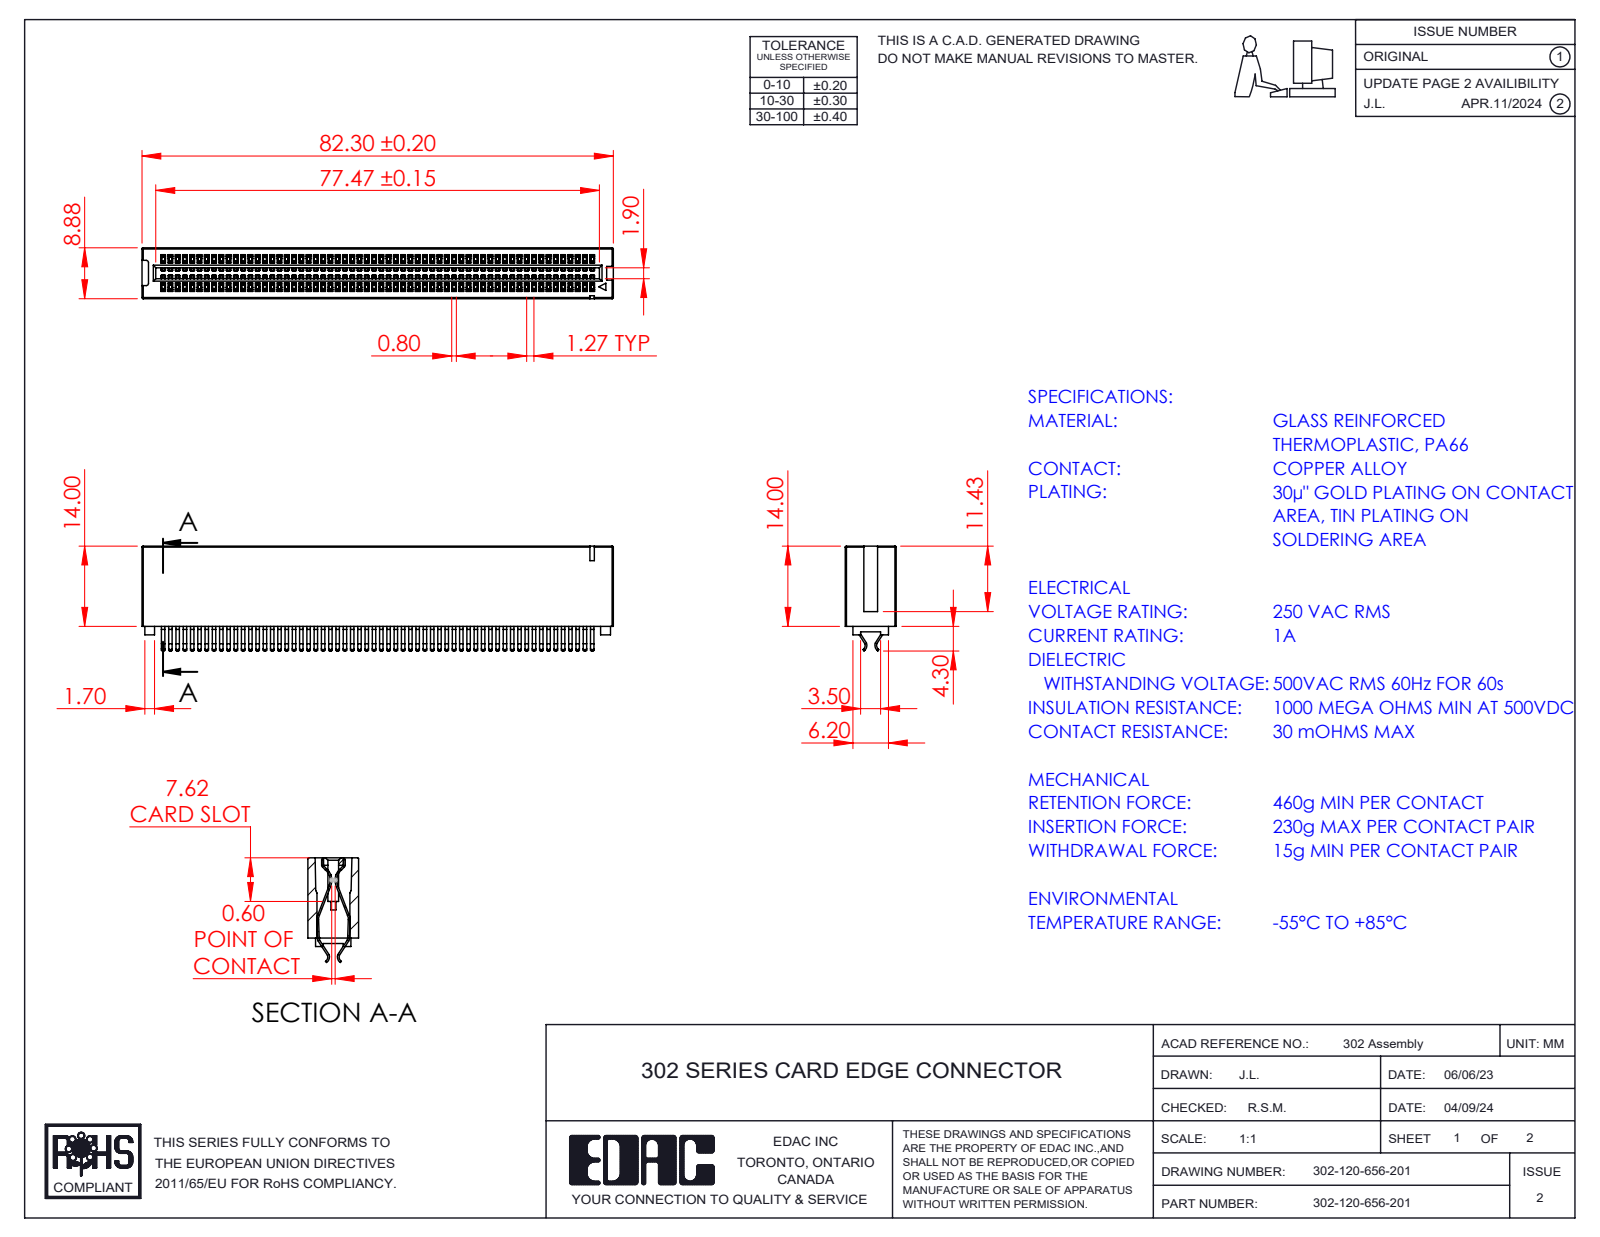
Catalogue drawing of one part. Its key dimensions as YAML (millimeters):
part_name: "302-120-656-201; Contact_302-290-X56; HSG_Vertical HSG"
step_written_by: "SolidWorks 2023 (CONFIG_CONTROL_DESIGN)"
units: millimeters
bodies: {solids: 121, faces: 5766, planar: 3829, cylindrical: 1933, other: 4}
overall_size: [82.3, 18.3, 8.88]
volume: 6275
surface_area: 18135
partial_cylinders:
  - {radius: 0.2, count: 368}
  - {radius: 0.11, count: 2}
  - {radius: 0.4, count: 2}
  - {radius: 0.41, count: 2}
  - {radius: 0.93, count: 2}
  - {radius: 1.05, count: 2}
  - {radius: 1.23, count: 2}
  - {radius: 1.25, count: 2}
face_to_face_distances: [8.88, 1.27, 2.54, 3.81, 5.08, 7.62, 6.35, 8.89, 10.16, 12.7]
